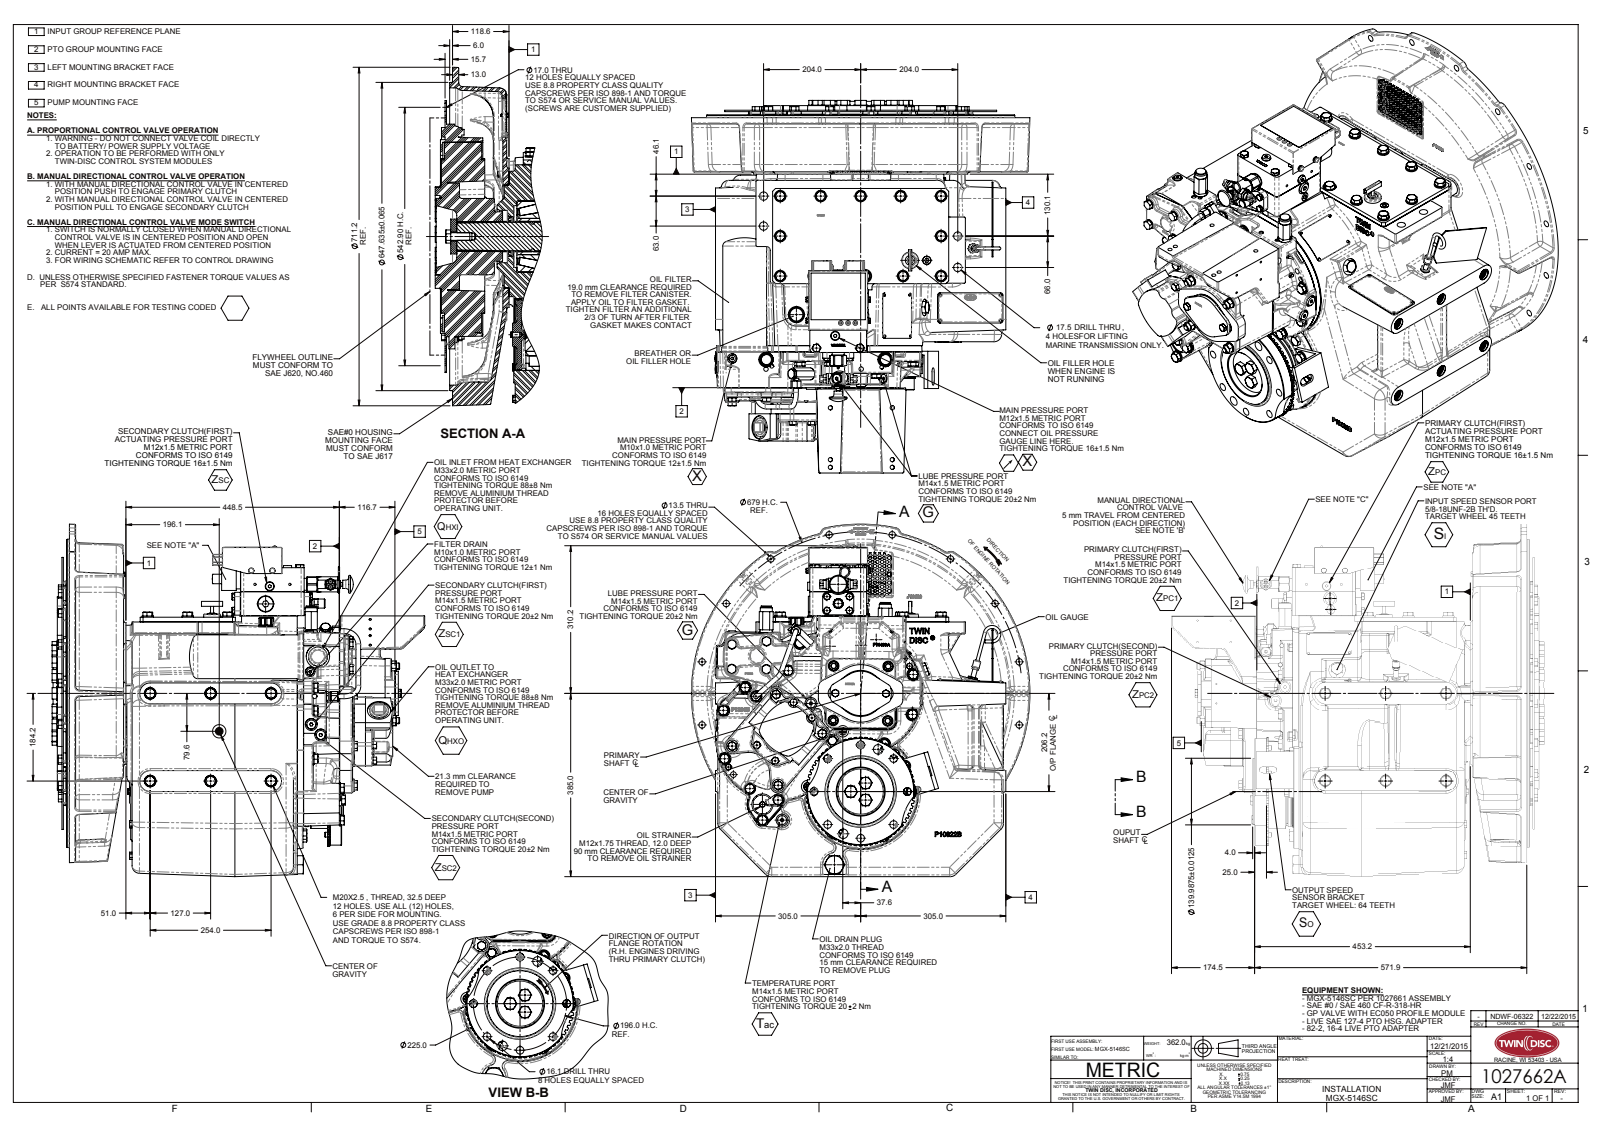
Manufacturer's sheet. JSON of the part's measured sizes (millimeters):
{"part_name": "1027662A", "step_written_by": "SolidWorks 2010 (AUTOMOTIVE_DESIGN)", "units": "millimeters", "bodies": {"solids": 0, "faces": 10083, "planar": 6327, "cylindrical": 1956, "other": 1800}, "overall_size": [939.8, 782.82, 729.7], "round_holes": [[7, 106], [13.5, 16], [17, 12], [4.2, 8], [16.1, 8], [25, 8], [8.8, 6], [23.51, 6], [12, 4], [17.5, 4], [20, 4], [9.34, 3]], "round_bosses_or_shafts": [[24, 31], [29.99, 16], [12, 10], [81, 8], [18.9, 7], [2.54, 5], [19.85, 4], [18.8, 4]], "partial_cylinders_radius": [[2.5, 109], [8, 85], [39.71, 67], [2, 49], [6.5, 48], [3, 44], [16, 32], [3.5, 26]], "face_to_face_distances": [8, 0.39, 378.38, 377.99, 364.9, 386.38, 385.99, 360.48, 360.09, 17.9], "hole_center_spacings": [627.73, 132.55, 564.94, 666.4, 10, 20, 30, 40]}
